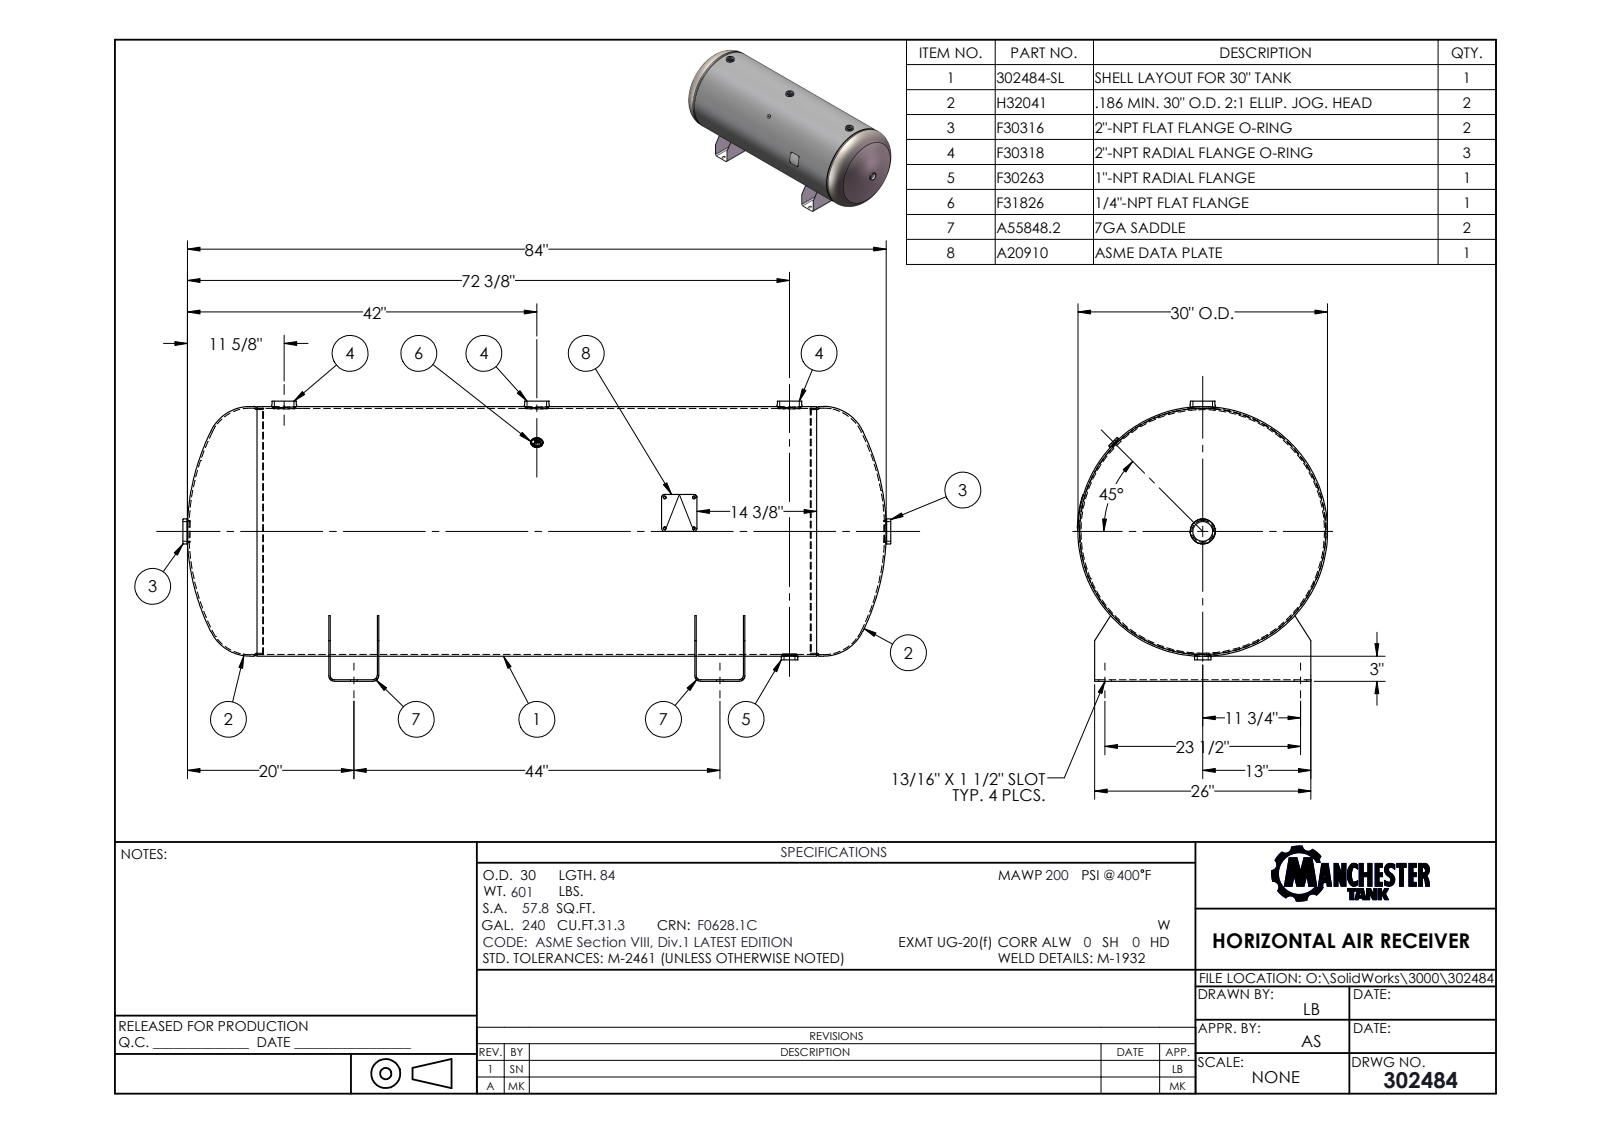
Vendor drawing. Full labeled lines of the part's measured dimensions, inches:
Part name (STEP PRODUCT): 302484
STEP written by: SolidWorks 2011 (CONFIG_CONTROL_DESIGN)
Units: inches
Bodies: 0 solids, 209 faces (64 planar, 81 cylindrical, 64 other)
Overall size (bounding box): 85.25 × 33.873 × 30
Round holes (diameter × count): ⌀2.375 ×4, ⌀0.54 ×1, ⌀1 ×1, ⌀1.315 ×1, ⌀29.546 ×1
Round bosses / shafts (diameter × count): ⌀3.625 ×2, ⌀30 ×1, ⌀29.63 ×1, ⌀3.625 ×1, ⌀3.5 ×1, ⌀2.875 ×1, ⌀1.5 ×1
Partial cylindrical surfaces — rounded edges, fillets, slot ends (radius × count): R0.406 ×8, R0.094 ×4, R0.281 ×4, R0.5 ×4, R15.06 ×1
Main face-to-face distances: 44, 0.187, 5.813, 0.188, 38.187, 6, 44.187, 49.813, 5.625, 43.813
Hole centre spacings: 30.375, 60.75
